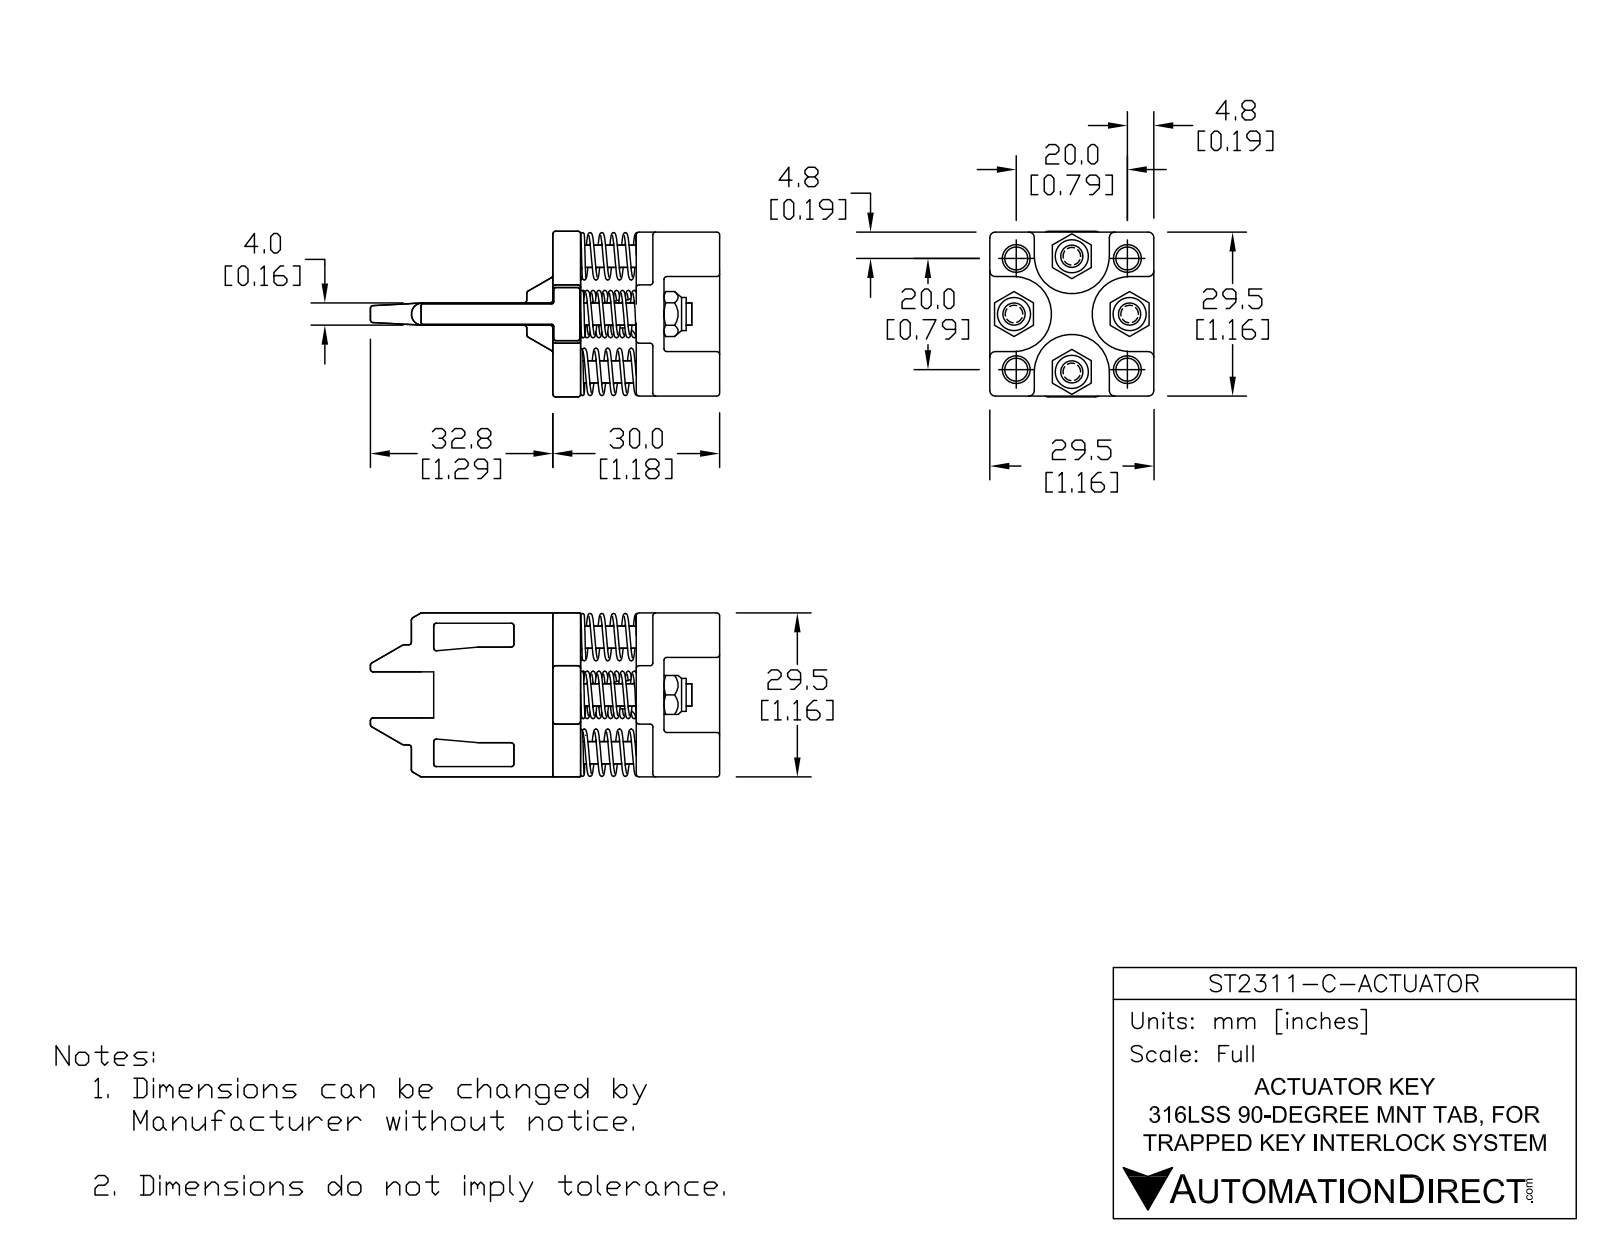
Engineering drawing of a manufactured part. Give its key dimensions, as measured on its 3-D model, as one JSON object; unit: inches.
{"part_name": "ST2311-C-ACTUATOR", "step_written_by": "SolidWorks 2017 (AUTOMOTIVE_DESIGN)", "units": "inches", "bodies": {"solids": 10, "faces": 595, "planar": 131, "cylindrical": 216, "other": 248}, "overall_size": [2.474, 1.173, 1.161], "volume_in3": 0.749, "surface_area_in2": 16.53, "round_holes": [[0.128, 4], [0.163, 4], [0.228, 4], [0.079, 1]], "round_bosses_or_shafts": [[0.157, 5], [0.234, 4], [0.197, 1]], "partial_cylinders_radius": [[0.02, 84], [0.039, 32], [0.035, 12], [0.012, 10], [0.266, 4], [0.016, 2]], "face_to_face_distances": [0.591, 0.787, 0.197, 1.161, 0.157, 0.394, 0.472, 0.502, 0.374, 0.659], "hole_center_spacings": [0.394, 0.894, 0.409, 0.557, 0.579, 0.787, 0.819, 1.113]}
